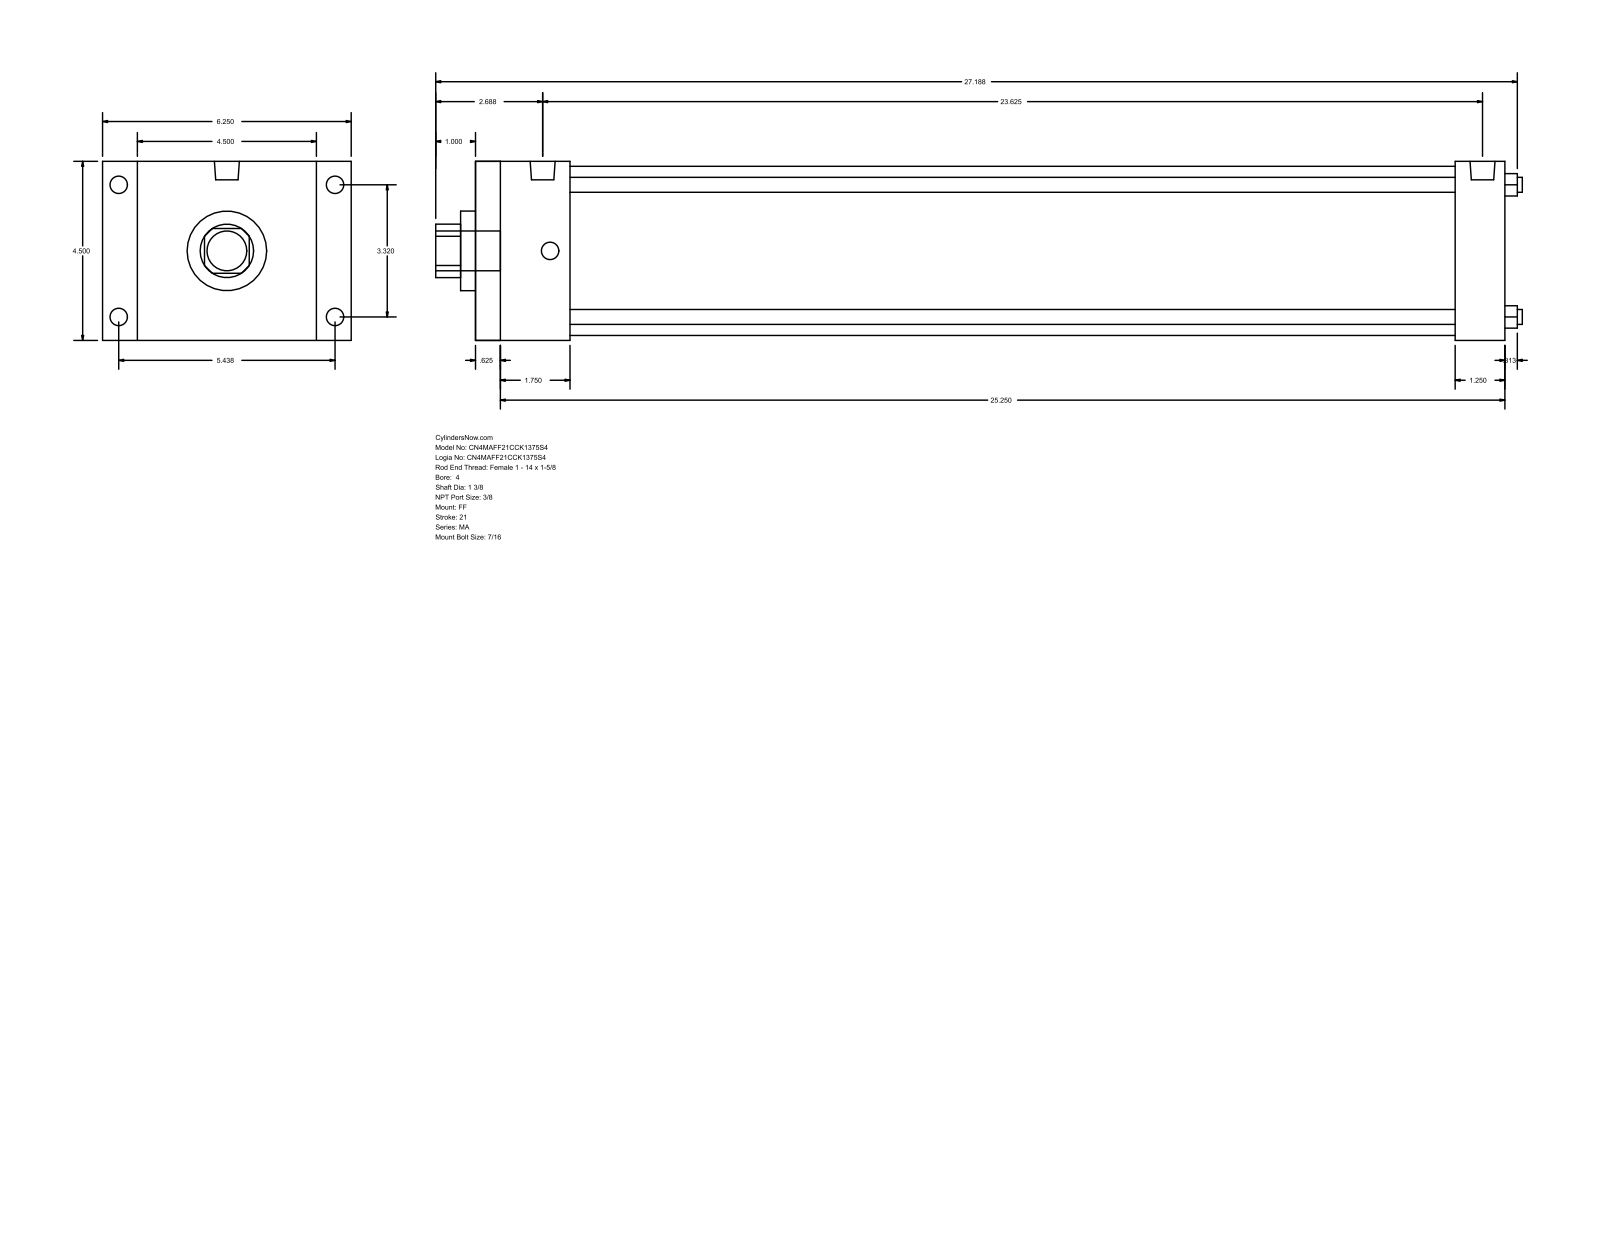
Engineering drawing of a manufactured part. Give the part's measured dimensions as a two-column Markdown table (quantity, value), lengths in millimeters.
| quantity | value |
| --- | --- |
| part name | MA_FF__0400_1.375 |
| STEP written by | GSSL Pune (CONFIG_CONTROL_DESIGN) |
| units | millimeters |
| bodies | 0 solids, 92 faces (64 planar, 28 cylindrical, 0 other) |
| overall size | 693.74 × 158.75 × 114.3 |
| round holes (diameter × count) | 9.53 × 4, 34.92 × 1, 50.8 × 1, 107.95 × 1 |
| round bosses / shafts (diameter × count) | 11.11 × 8, 15.93 × 2, 25.4 × 1 |
| partial cylindrical surfaces (radius × count) | 17.06 × 1 |
| main face-to-face distances | 114.3, 657.22, 15.87, 641.35, 22.23, 136.53, 625.48, 609.61, 31.74, 60.32 |
| hole center spacings | 59.62, 84.32, 119.25 |
